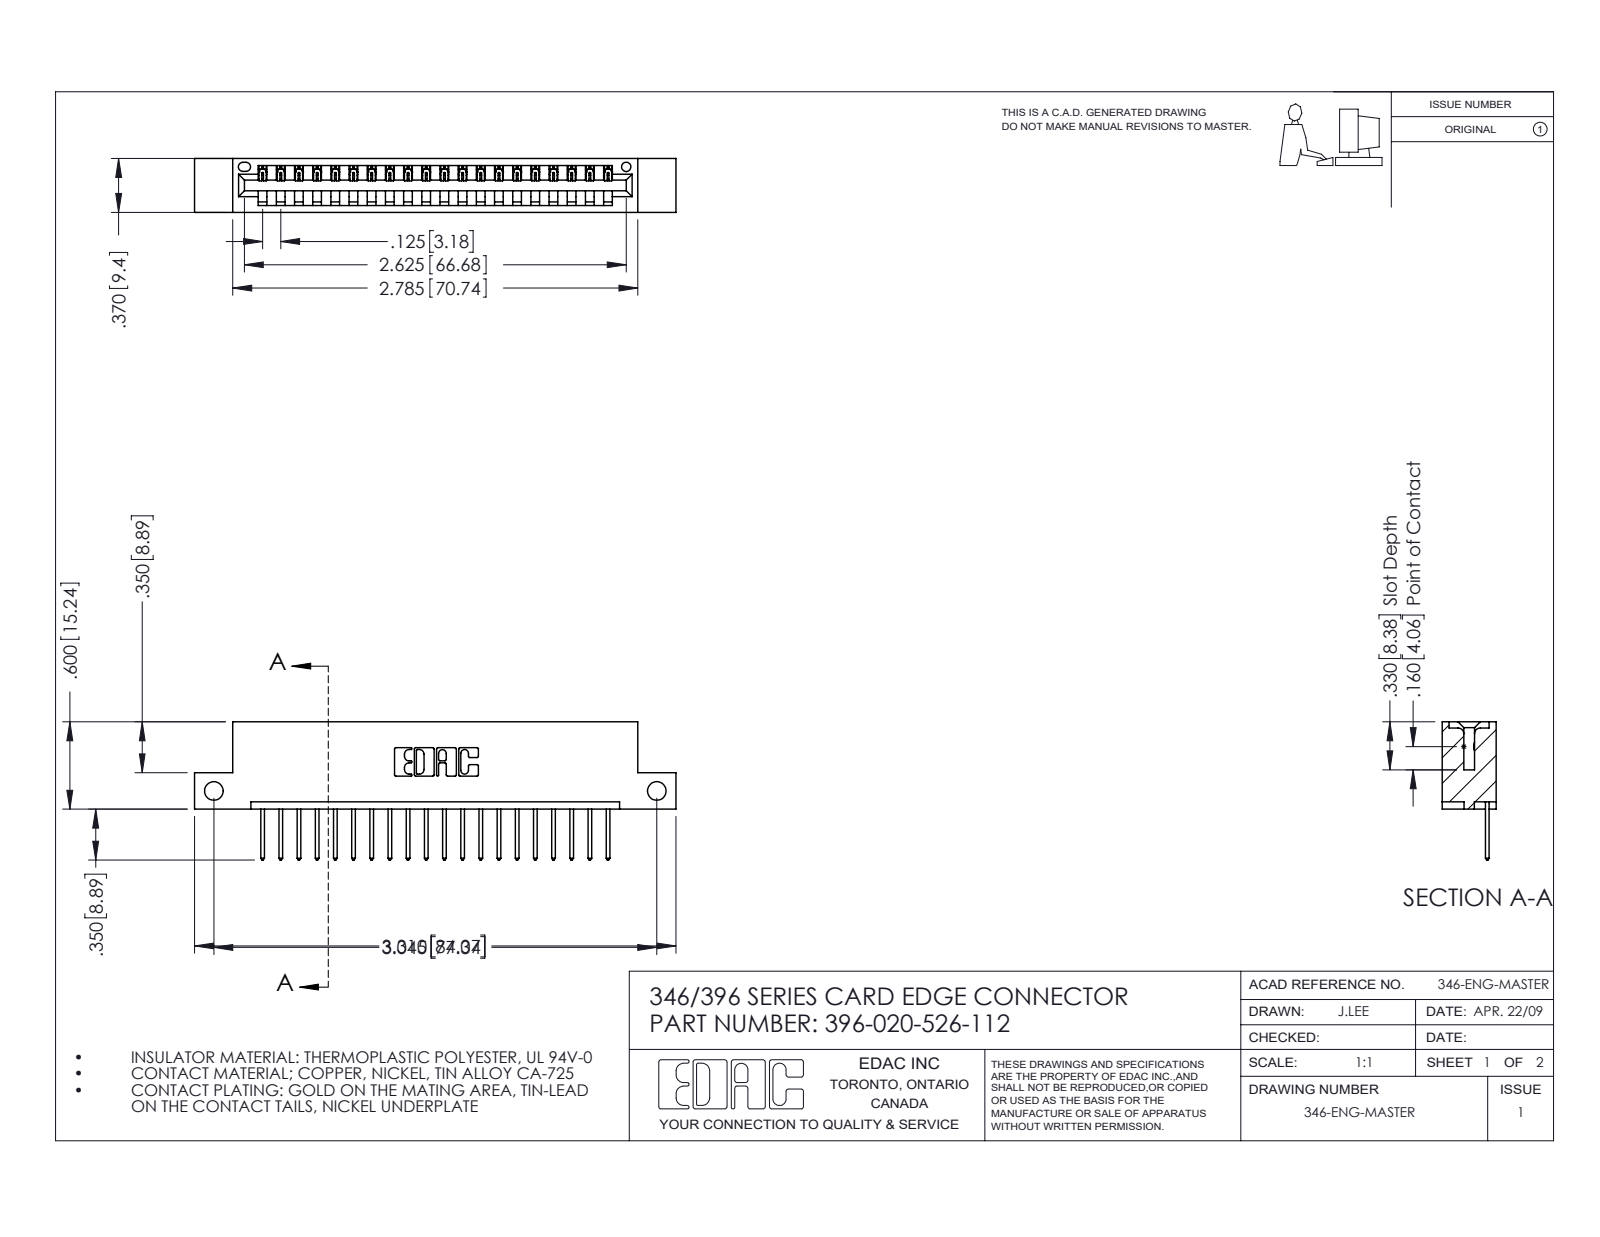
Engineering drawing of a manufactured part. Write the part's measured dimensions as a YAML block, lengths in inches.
part_name: "396-020-526-112; 345-292-001_345-293-126; 346 Part_Flush Mounting Lugs - Side Mount"
step_written_by: "SolidWorks 2016 (CONFIG_CONTROL_DESIGN)"
units: inches
bodies: {solids: 21, faces: 1282, planar: 876, cylindrical: 406, other: 0}
overall_size: [3.31, 0.95, 0.37]
volume: 0.476
surface_area: 14.47
round_holes:
  - {diameter: 0.128, count: 2}
  - {diameter: 0.064, count: 1}
partial_cylinders:
  - {radius: 0.006, count: 40}
  - {radius: 0.01, count: 40}
  - {radius: 0.01, count: 22}
  - {radius: 0.007, count: 6}
  - {radius: 0.031, count: 6}
  - {radius: 0.026, count: 3}
  - {radius: 0.031, count: 2}
  - {radius: 0.04, count: 2}
face_to_face_distances: [0.048, 0.322, 0.25, 0.37, 0.072, 0.298, 0.025, 0.148, 0.222, 0.1]
hole_center_spacings: [3.045]
